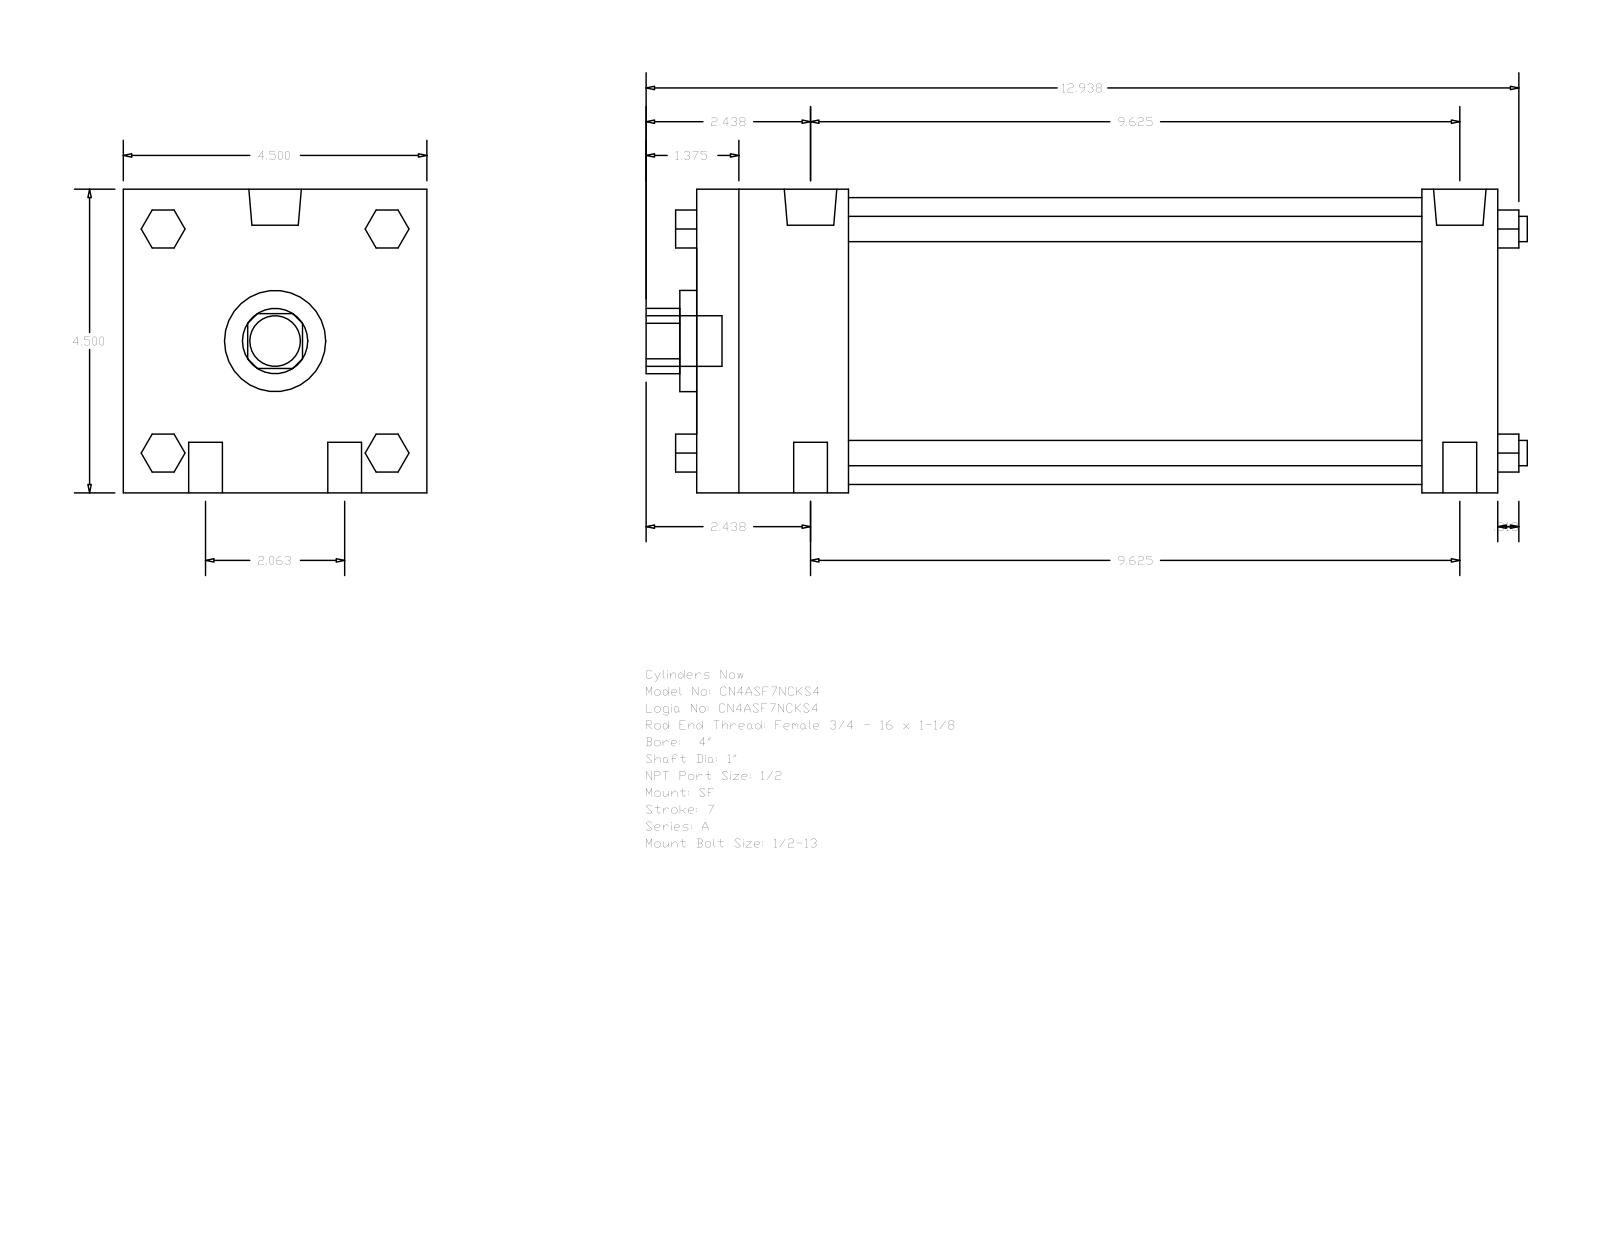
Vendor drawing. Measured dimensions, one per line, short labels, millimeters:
name: A_SF__0400_1
written by: GSSL Pune (CONFIG_CONTROL_DESIGN)
unit: mm
bodies: 0 solids, 124 faces (94 planar, 30 cylindrical, 0 other)
size: 331.79 × 114.3 × 114.3
holes: 1× ⌀25.4, 1× ⌀38.1, 1× ⌀107.95
bosses: 4× ⌀12.7, 4× ⌀9.53, 2× ⌀19.77, 2× ⌀8.73, 1× ⌀19.05
rounds: 1× R12.29
face distances: 114.3, 301.63, 273.05, 28.58, 57.15, 215.9, 244.48, 14.29, 42.16, 73.03
